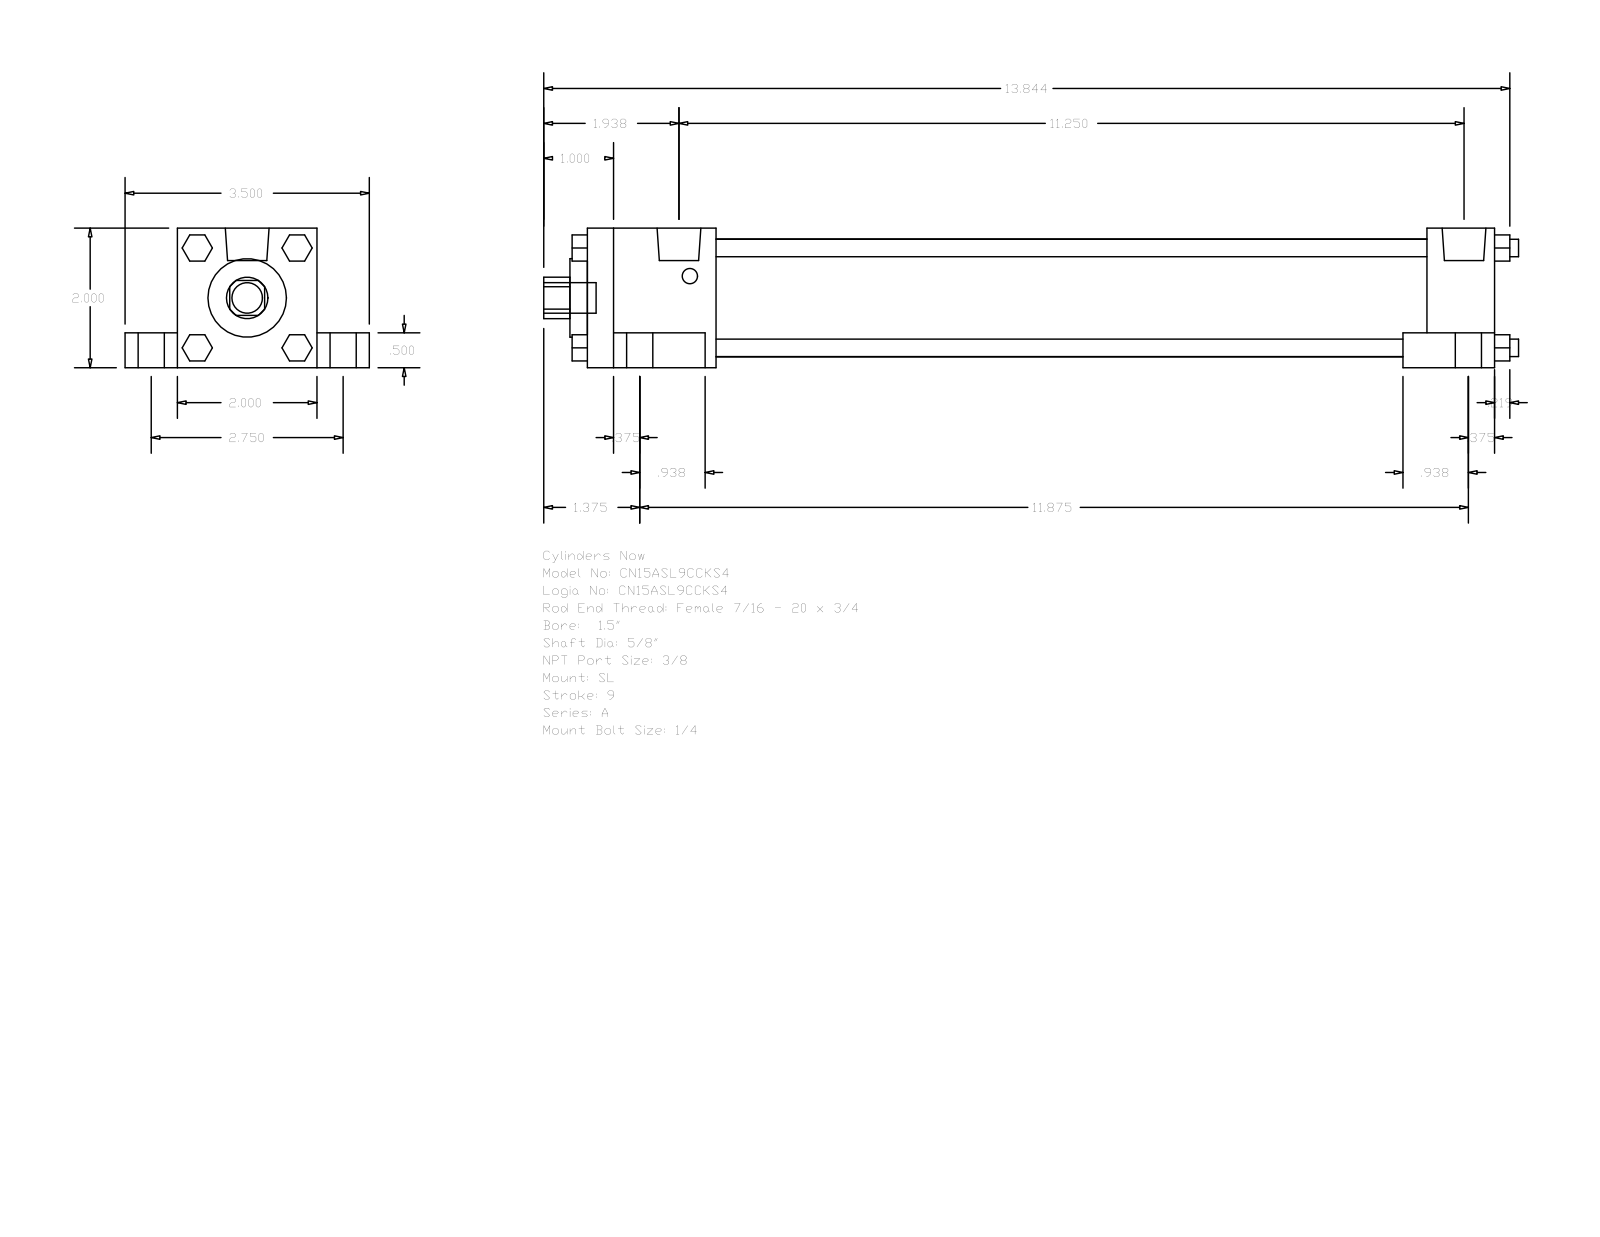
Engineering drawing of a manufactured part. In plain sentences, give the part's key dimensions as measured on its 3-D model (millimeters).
The part is named "A_SL__0150_0.625". Its 3-D file was written by "GSSL Pune (CONFIG_CONTROL_DESIGN)". It is 0 solids with 148 faces: 112 planar, 36 cylindrical and 0 other. Overall it measures 354.81 by 88.9 by 50.8 millimeters. Round holes: 1 of diameter 15.88, 1 of diameter 28.57, 1 of diameter 42.93. Round bosses or shafts: 4 of diameter 15.88, 4 of diameter 9.53, 4 of diameter 6.35, 4 of diameter 5.56, 2 of diameter 15.93, 1 of diameter 11.11. Partial cylindrical surfaces (rounded edges, fillets, slot ends): 1 of radius 7.54. The main face-to-face distances are 50.8, 19.05, 12.7, 38.1, 69.85, 330.19, 9.52, 305.59, 24.6, 46.83.
